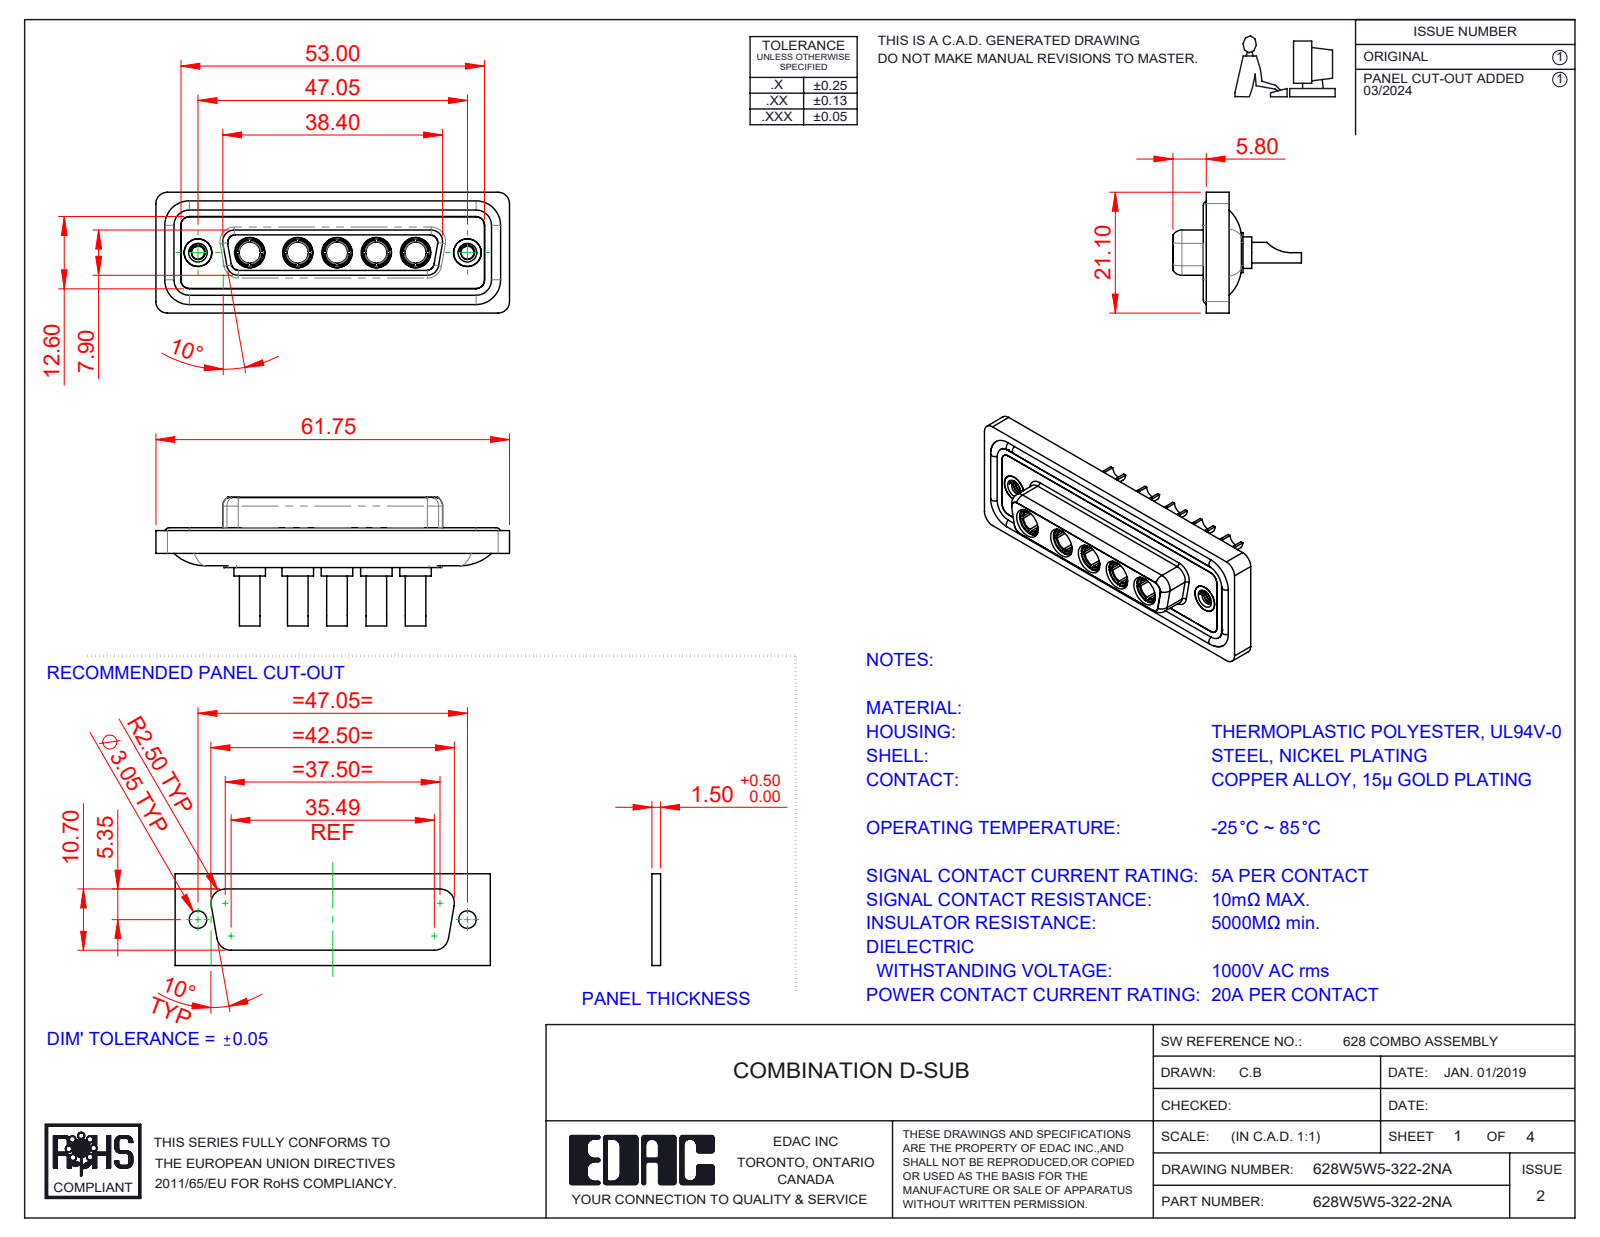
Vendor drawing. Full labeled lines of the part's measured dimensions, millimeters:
Part name (STEP PRODUCT): 628Combo Housing_5W5; 628W5W5-322-2NA; 628Combo Shell Front_25 Contacts; 628Combo Shell Rear_25 Contacts (+3 more)
STEP written by: SolidWorks 2023 (CONFIG_CONTROL_DESIGN)
Units: millimetres
Bodies: 17 solids, 784 faces (265 planar, 320 cylindrical, 199 other)
Overall size (bounding box): 61.75 × 22.45 × 21.1
Volume: 8 238 mm³ · Surface area: 13 825 mm²
Round holes (diameter × count): ⌀4.85 ×7, ⌀2.7 ×5, ⌀3.7 ×5, ⌀5.3 ×5, ⌀2.26 ×2, ⌀4 ×2, ⌀4.05 ×2, ⌀5 ×2
Round bosses / shafts (diameter × count): ⌀5.5 ×5, ⌀5.2 ×5, ⌀4.96 ×5, ⌀4.75 ×5, ⌀3.75 ×5, ⌀3.6 ×5, ⌀1.6 ×4, ⌀4.95 ×2
Partial cylindrical surfaces — rounded edges, fillets, slot ends (radius × count): R1.5 ×22, R2 ×18, R1.35 ×8, R1.6 ×8, R2.1 ×5, R0.25 ×4, R0.5 ×4, R0.6 ×4
Main face-to-face distances: 0.4, 1.8, 7.45, 5.65, 0.5, 7.05, 6.6, 1.6, 1.1, 2.9
Hole centre spacings: 6.86, 9.04, 13.72, 38.01, 8.39, 15.25, 15.9, 17.43
